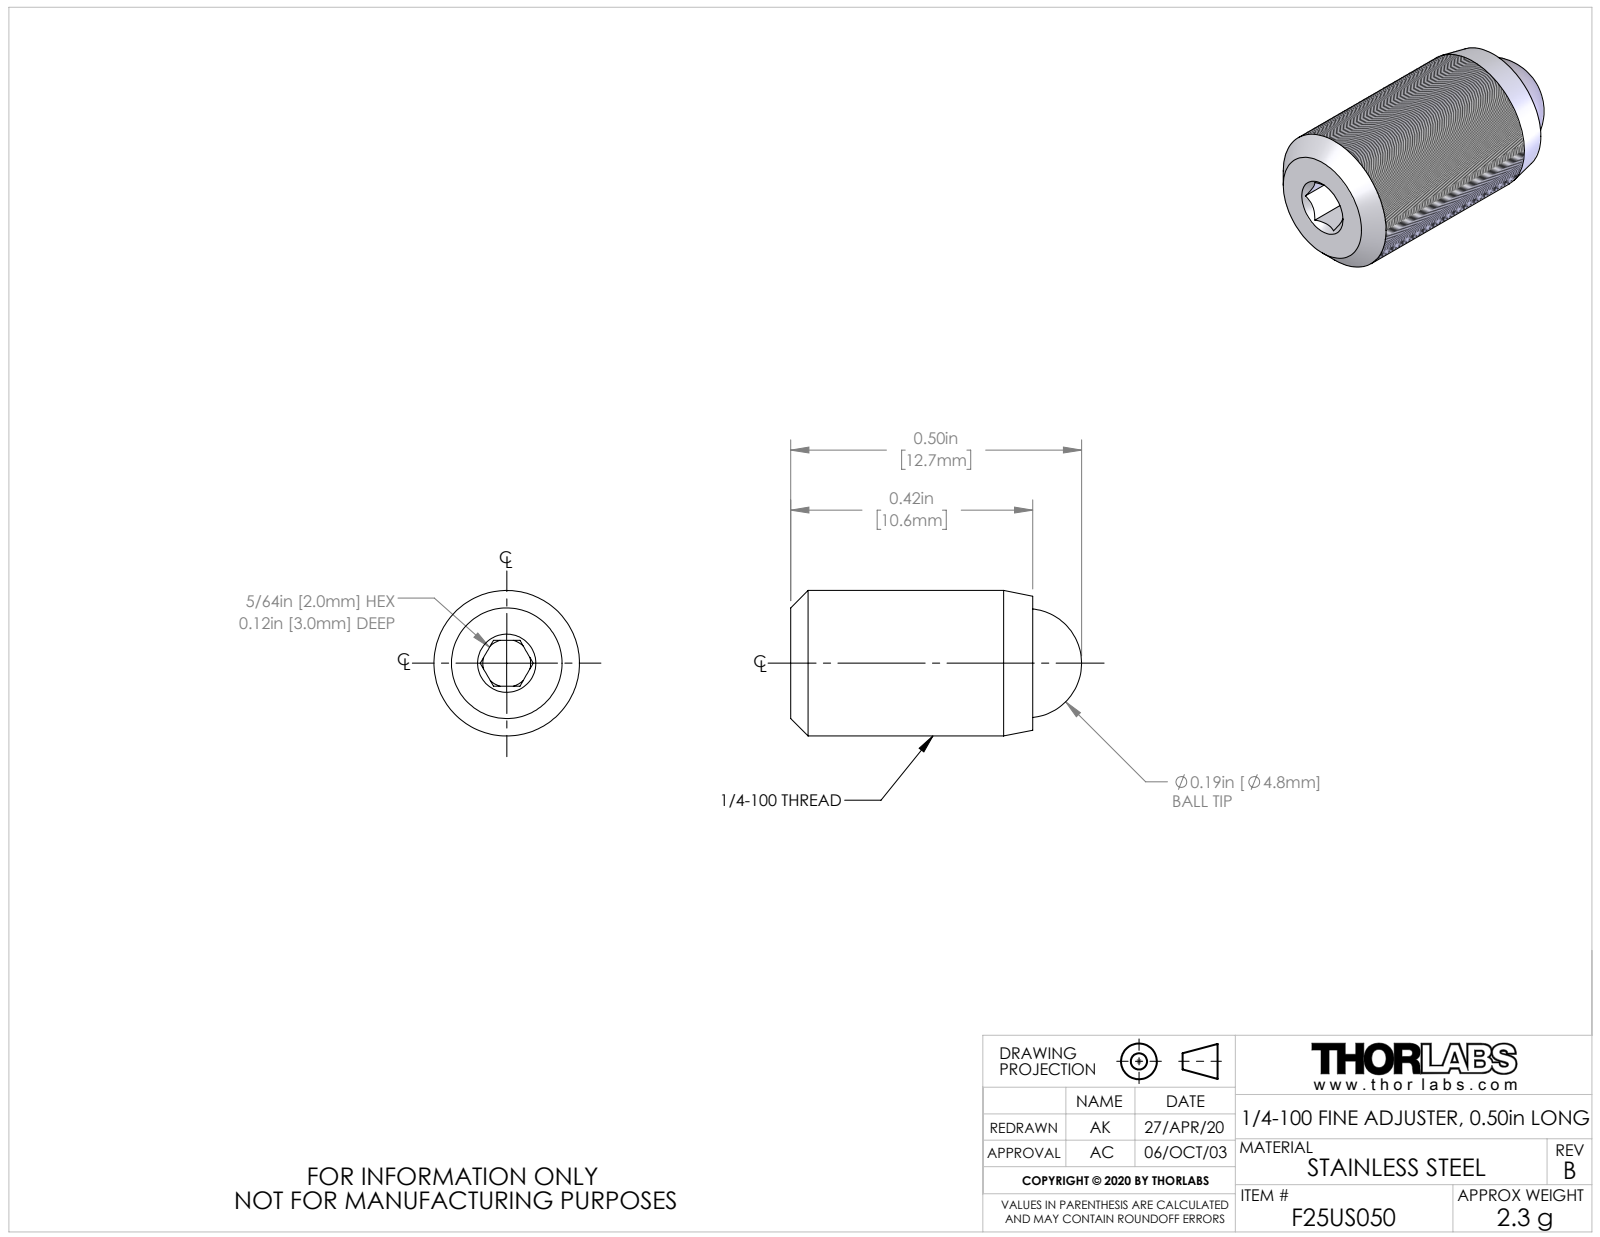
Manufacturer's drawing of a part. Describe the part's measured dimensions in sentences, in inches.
The part is named "7641-E0W". Its 3-D file was written by "SolidWorks 2018 (AUTOMOTIVE_DESIGN)". It is 2 solids with 38 faces: 20 planar, 6 cylindrical and 12 other. Overall it measures 0.5 by 0.25 by 0.25 inches. Its volume is 0.02 cubic inches and its surface area 0.594 square inches. Round holes: 1 of diameter 0.082, 1 of diameter 0.188. Round bosses or shafts: 1 of diameter 0.25. The main face-to-face distances are 0.079, 0.416, 0.296, 0.12.
